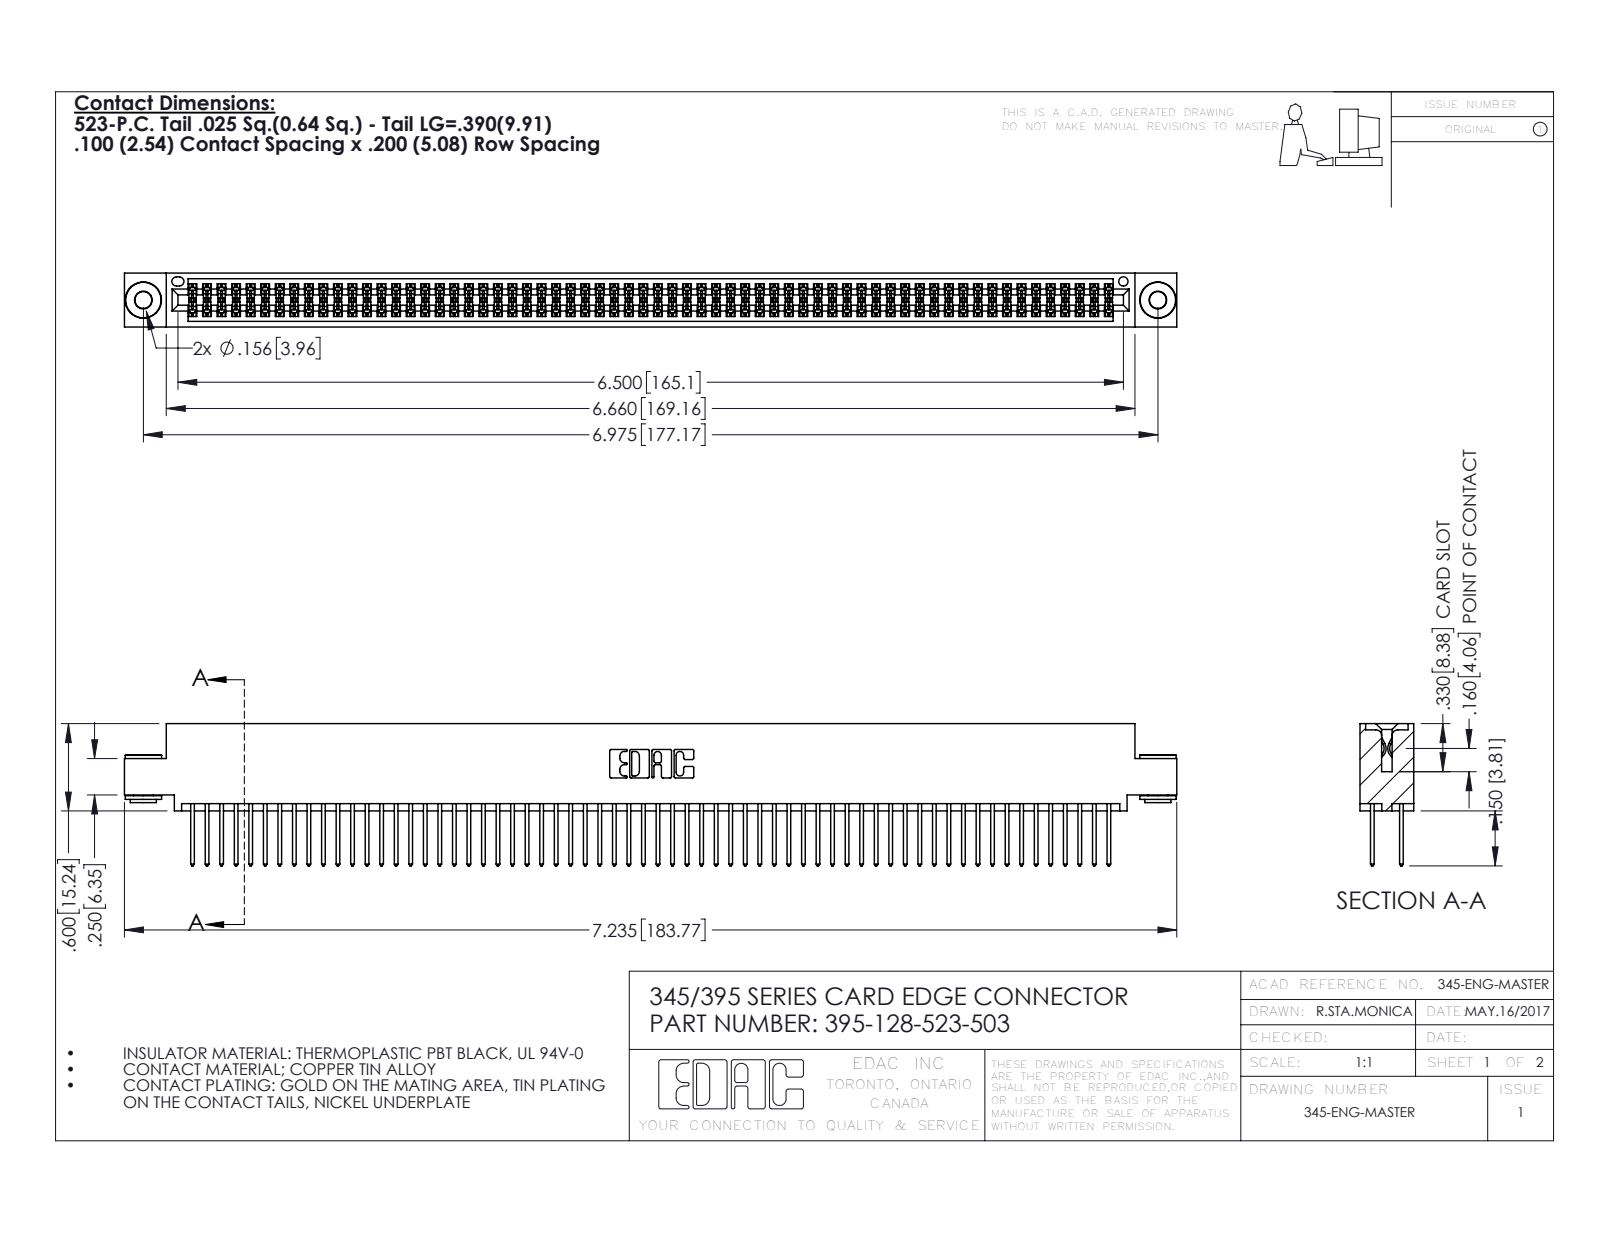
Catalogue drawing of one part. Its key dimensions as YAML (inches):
part_name: "395-128-523-503; 345 Part_0.110 Offset - 0.156 Dia-TH; 345-250-002_345-250-002-102; 345-292-001_345-293-123"
step_written_by: "SolidWorks 2016 (CONFIG_CONTROL_DESIGN)"
units: inches
bodies: {solids: 131, faces: 6568, planar: 4318, cylindrical: 2242, other: 8}
overall_size: [7.235, 0.977, 0.37]
volume: 1.115
surface_area: 44.79
round_holes:
  - {diameter: 0.116, count: 2}
  - {diameter: 0.156, count: 2}
  - {diameter: 0.064, count: 1}
round_bosses_or_shafts:
  - {diameter: 0.25, count: 2}
  - {diameter: 0.18, count: 2}
  - {diameter: 0.136, count: 2}
partial_cylinders:
  - {radius: 0.006, count: 192}
  - {radius: 0.01, count: 128}
  - {radius: 0.01, count: 22}
  - {radius: 0.007, count: 6}
  - {radius: 0.031, count: 6}
  - {radius: 0.026, count: 3}
  - {radius: 0.014, count: 2}
  - {radius: 0.019, count: 2}
face_to_face_distances: [0.072, 0.298, 0.2, 0.025, 0.098, 0.272, 0.37, 0.225, 0.175, 0.149]
hole_center_spacings: [0.27, 6.739, 6.975]
